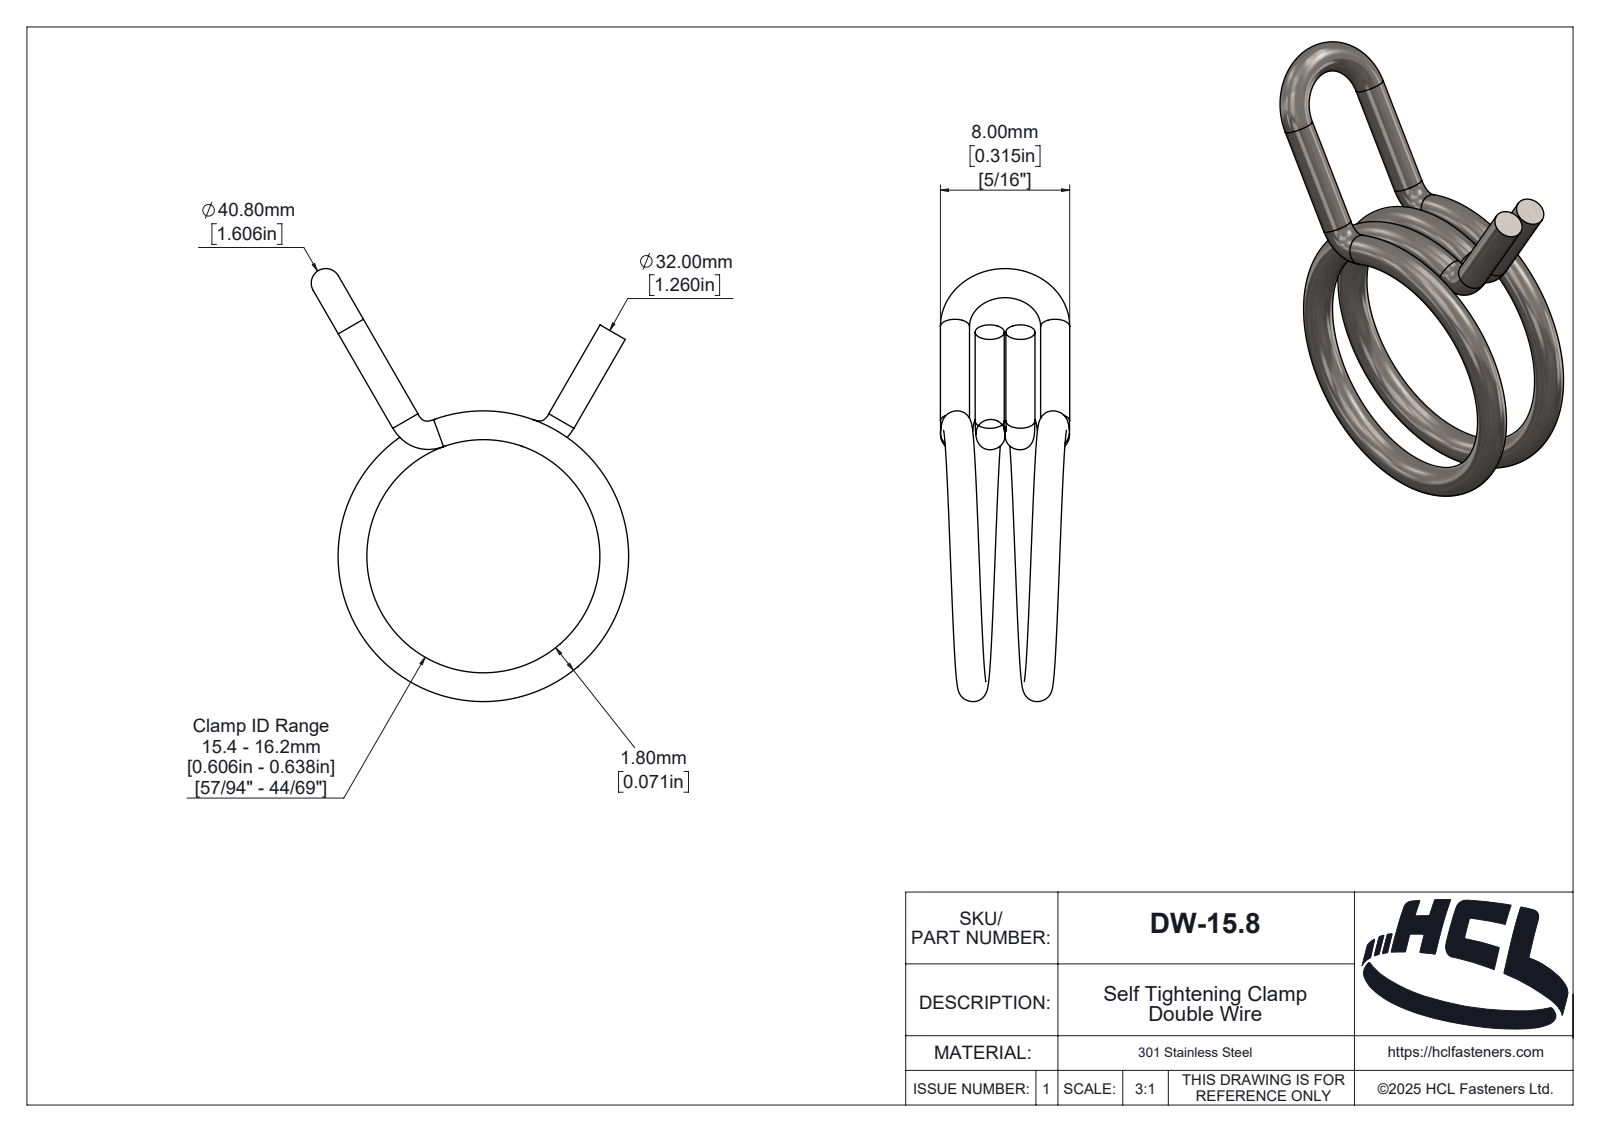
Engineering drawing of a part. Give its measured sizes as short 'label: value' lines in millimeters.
name: DW-15.8
written by: SolidWorks 2025 (AUTOMOTIVE_DESIGN)
unit: mm
bodies: 1 solid, 132 faces (14 planar, 53 cylindrical, 65 other)
size: 26.78 × 19.64 × 8
volume: 399 mm³; area: 897 mm²
bosses: 4× ⌀1.8
rounds: 1× R0.16, 1× R0.2, 1× R0.21, 1× R0.26, 1× R0.36, 1× R0.48, 1× R0.6, 1× R0.68
